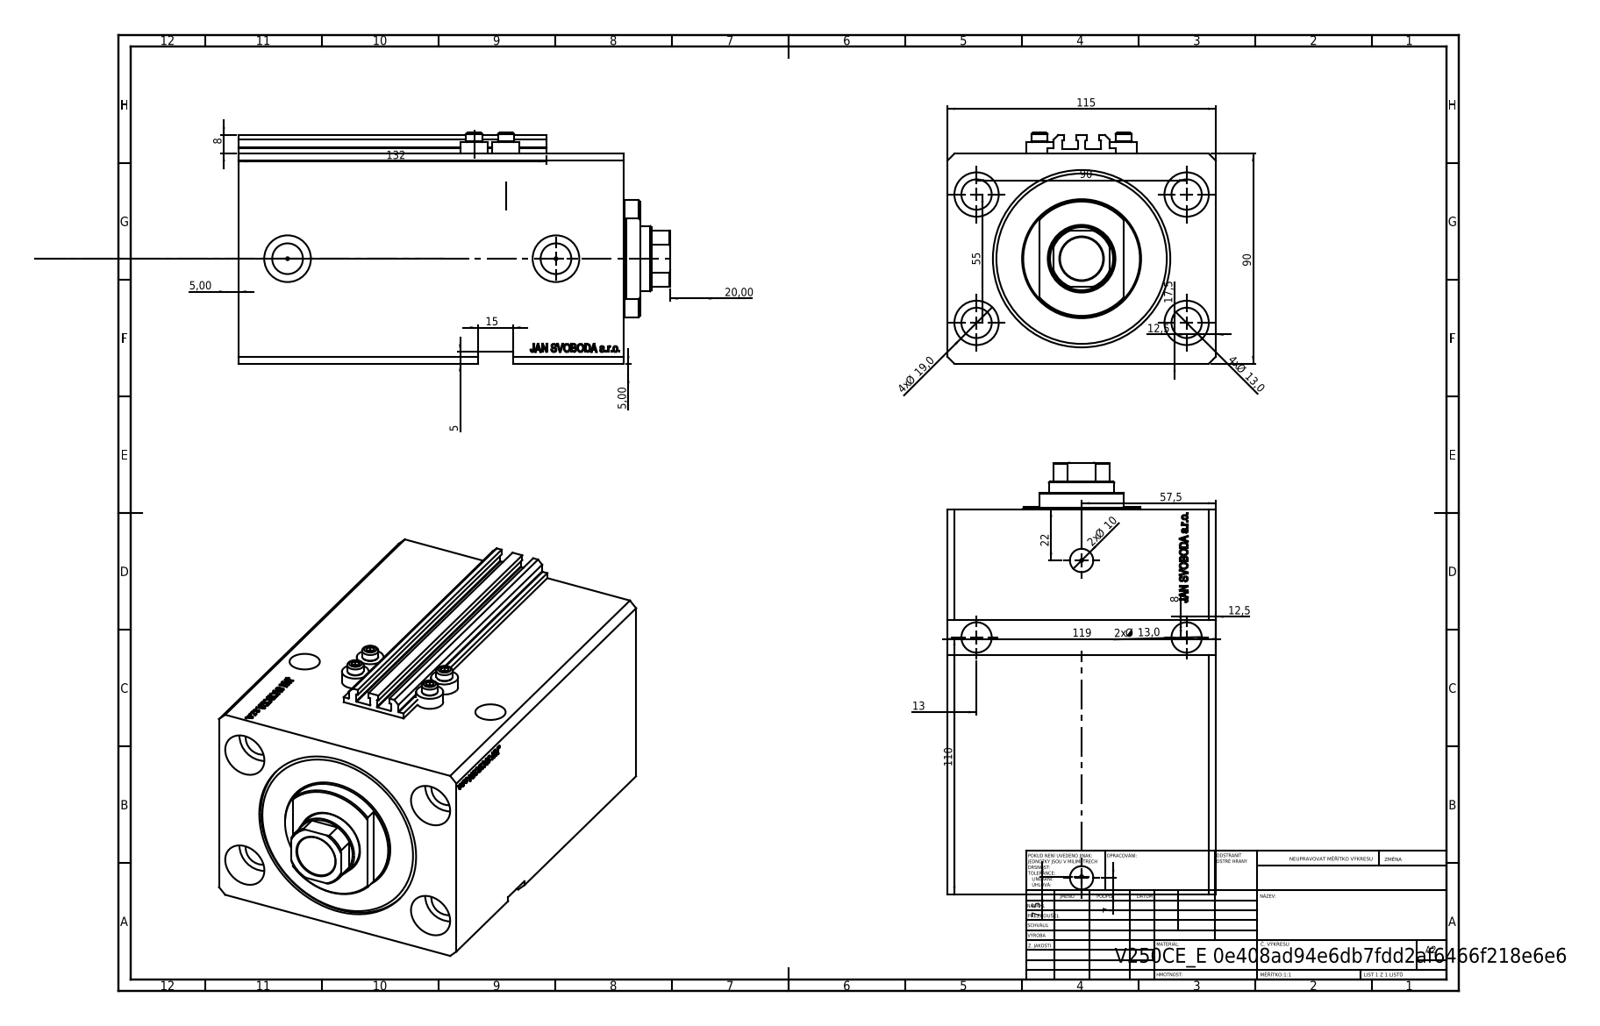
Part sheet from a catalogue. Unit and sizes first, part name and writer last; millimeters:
Units: millimetres
Overall size (bounding box): 184.9 × 115 × 99
Round holes (diameter × count): ⌀13 ×6, ⌀1.25 ×4, ⌀4 ×4, ⌀19 ×4, ⌀10 ×2, ⌀13.16 ×2, ⌀20 ×2, ⌀18.5 ×1, ⌀28 ×1, ⌀63 ×1, ⌀76 ×1
Round bosses / shafts (diameter × count): ⌀11.6 ×4, ⌀7 ×4, ⌀50 ×1
Partial cylindrical surfaces — rounded edges, fillets, slot ends (radius × count): R0.2 ×10, R13.5 ×1
Main face-to-face distances: 90, 115, 165, 17.9, 147.1, 117, 134.9, 30.1, 80, 54.9
Hole centre spacings: 52.74, 90, 13.6, 27.39, 28.46, 33.62, 36, 38.48
Volume: 1 400 000 mm³ · Surface area: 213 672 mm²
Bodies: 8 solids, 1107 faces (543 planar, 126 cylindrical, 438 other)
Part name (STEP PRODUCT): V250CE_E_Body; V250CE_VC_E; ALLEN BOLT V250CE; V250CE_C_VCP
STEP written by: SolidWorks 2019 (CONFIG_CONTROL_DESIGN)
